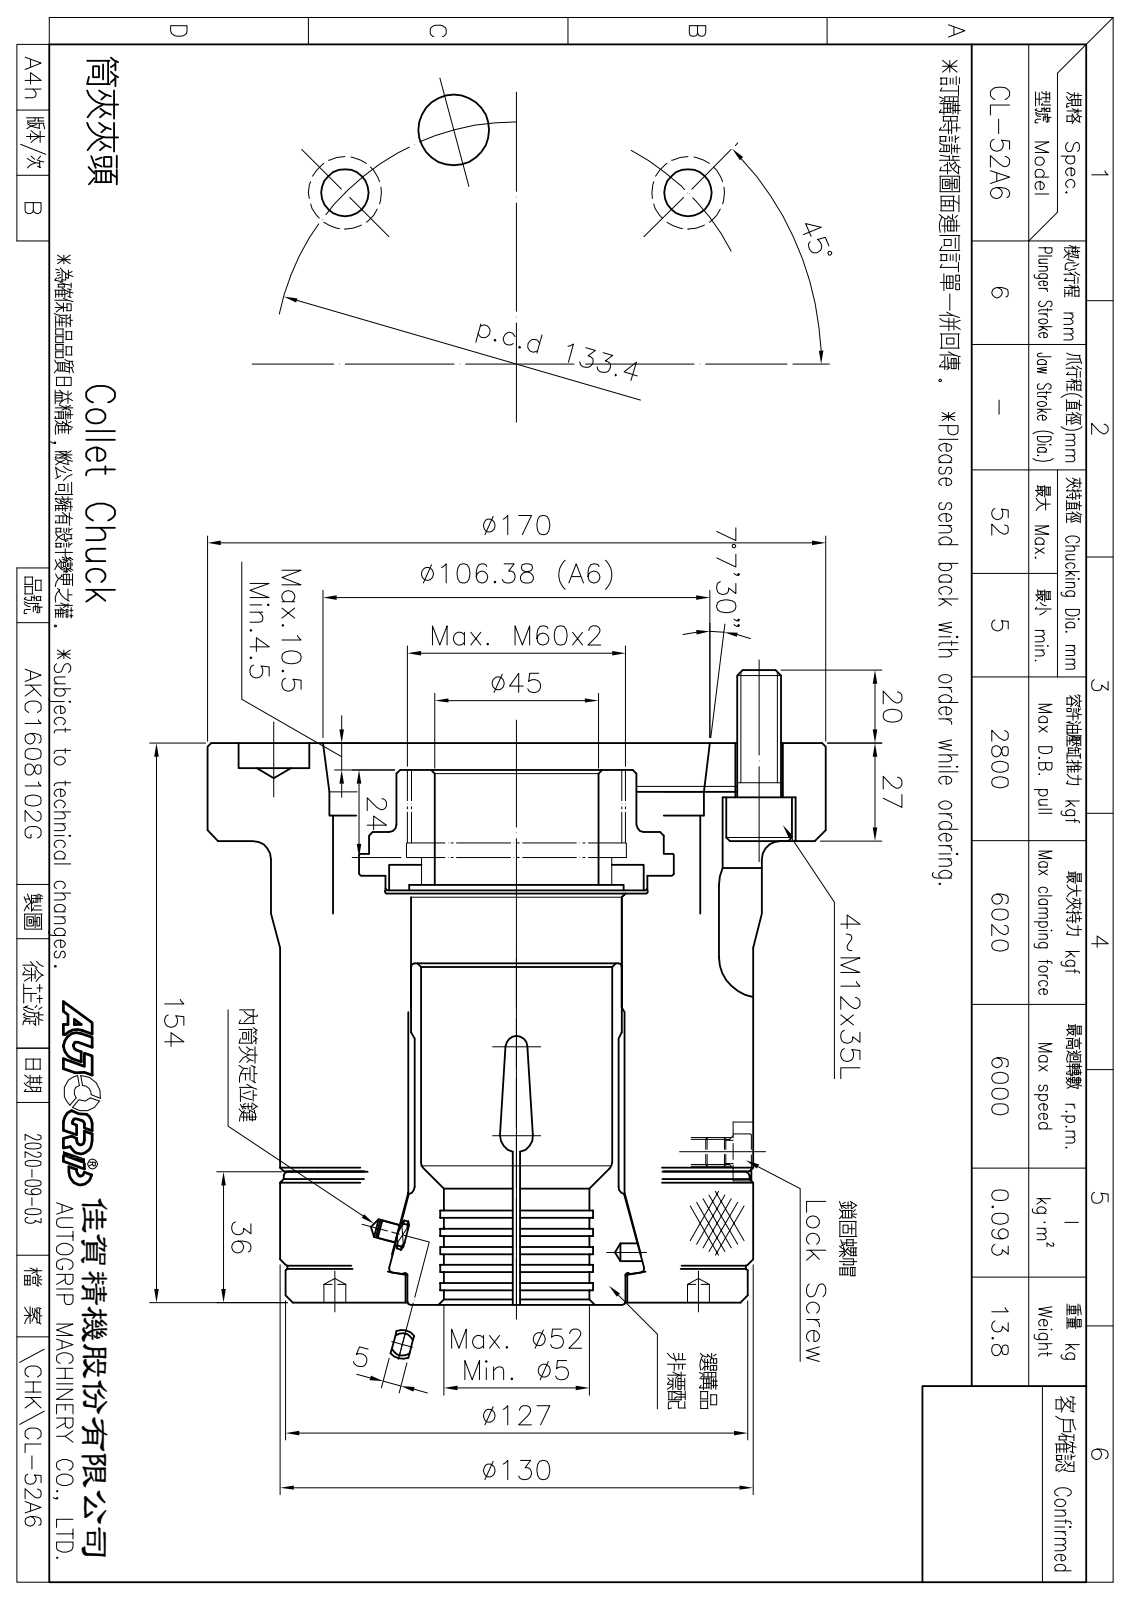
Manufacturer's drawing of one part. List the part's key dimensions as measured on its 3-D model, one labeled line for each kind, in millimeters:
Part name (STEP PRODUCT): CF-CL-52-03020; CF-CL-52-02000; CF-CL-60A6-01010; CF-CL-52A6 (+4 more)
STEP written by: SolidWorks 2016 (CONFIG_CONTROL_DESIGN)
Units: millimetres
Bodies: 10 solids, 385 faces (119 planar, 122 cylindrical, 144 other)
Overall size (bounding box): 173.8 × 170 × 170
Volume: 1 704 000 mm³ · Surface area: 286 639 mm²
Round holes (diameter × count): ⌀13.5 ×4, ⌀20 ×4, ⌀6 ×2, ⌀19.5 ×2, ⌀5 ×1, ⌀6.8 ×1, ⌀52.3 ×1, ⌀58 ×1, ⌀59 ×1, ⌀59.5 ×1, ⌀60.5 ×1, ⌀61 ×1
Round bosses / shafts (diameter × count): ⌀18 ×4, ⌀12 ×4, ⌀170 ×1, ⌀135 ×1, ⌀130 ×1, ⌀128 ×1, ⌀127 ×1, ⌀126 ×1
Partial cylindrical surfaces — rounded edges, fillets, slot ends (radius × count): R10 ×4, R8.5 ×3, R4 ×1, R8 ×1, R8.25 ×1
Main face-to-face distances: 117.8, 36, 153.8, 6.5, 27, 90.8, 126.8, 20, 33.5, 84.3
Hole centre spacings: 66.69, 94.32, 22.49, 34.53, 47.25, 50, 66.7, 72.26
